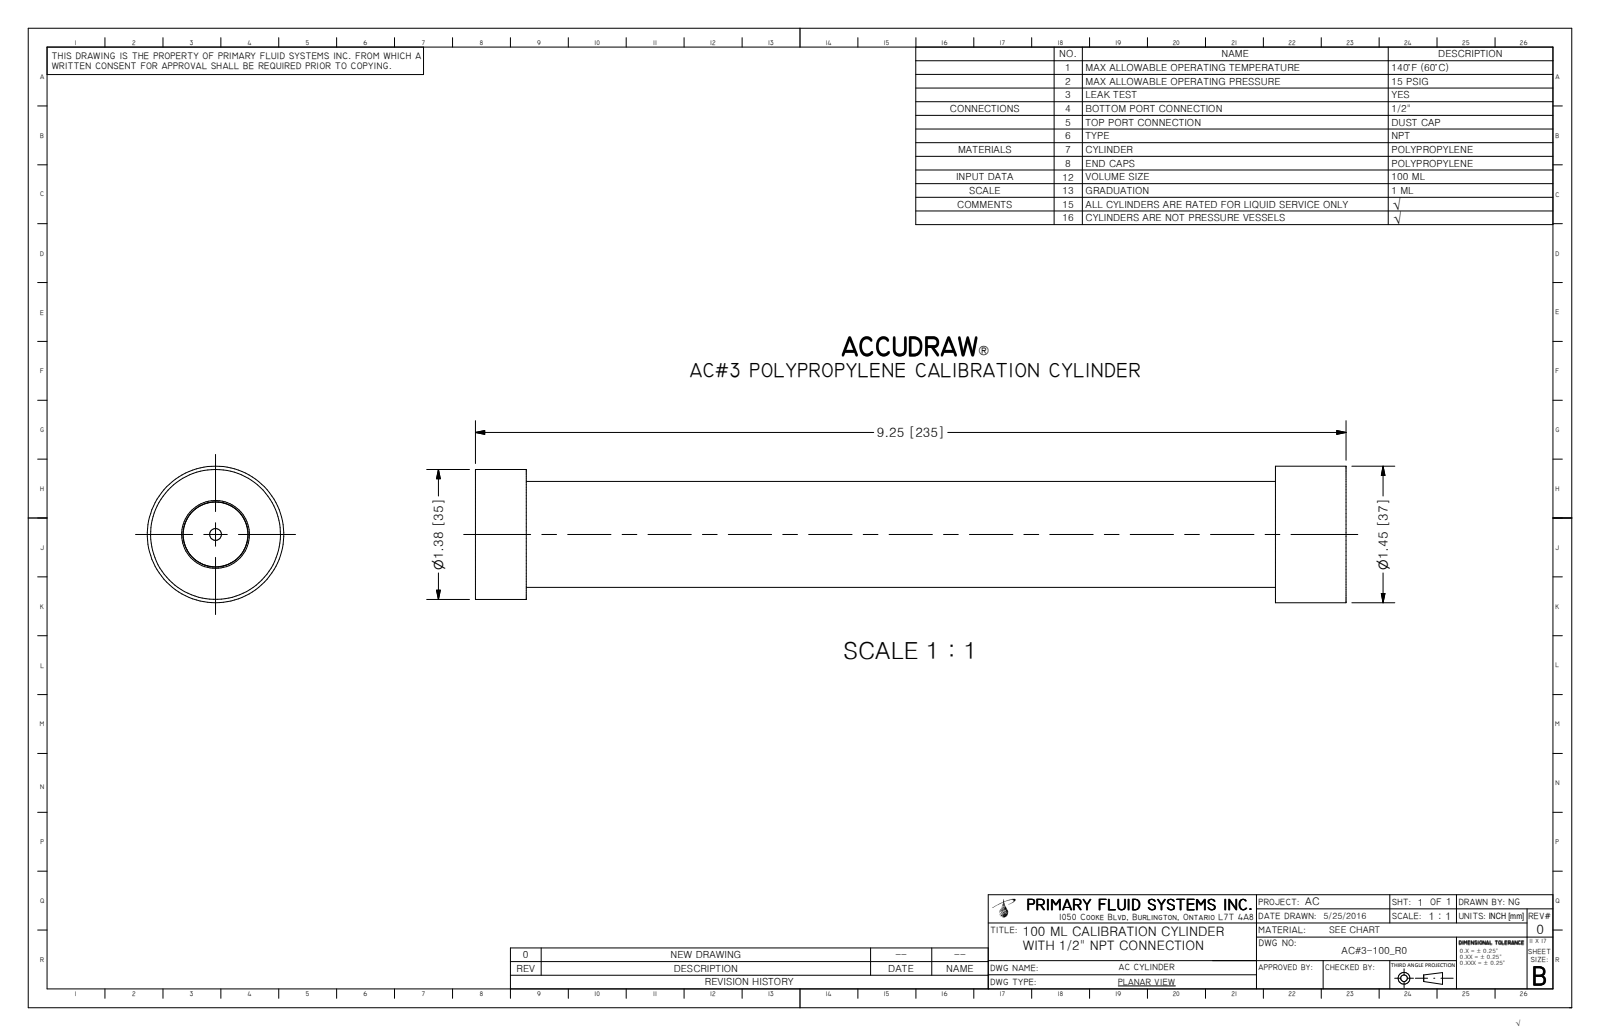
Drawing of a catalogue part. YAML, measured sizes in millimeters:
part_name: "AC#3-100_R0; AC-2B-100-S; AC-100-TUBE; AC-DC-100_R1"
step_written_by: "Autodesk Inventor 2009 (AUTOMOTIVE_DESIGN)"
units: millimeters
bodies: {solids: 3, faces: 20, planar: 10, cylindrical: 9, other: 1}
overall_size: [230.8, 36.8, 36.8]
volume: 55400
surface_area: 46390
round_holes:
  - {diameter: 17.5, count: 1}
  - {diameter: 21.3, count: 1}
  - {diameter: 25.5, count: 1}
  - {diameter: 30.5, count: 1}
round_bosses_or_shafts:
  - {diameter: 36.8, count: 1}
  - {diameter: 35.1, count: 1}
  - {diameter: 28.6, count: 1}
  - {diameter: 27.4, count: 1}
  - {diameter: 25.7, count: 1}
face_to_face_distances: [19.1, 211.7, 230.8, 13.7, 198, 217, 5.3, 192.7, 221.2, 207.5]
